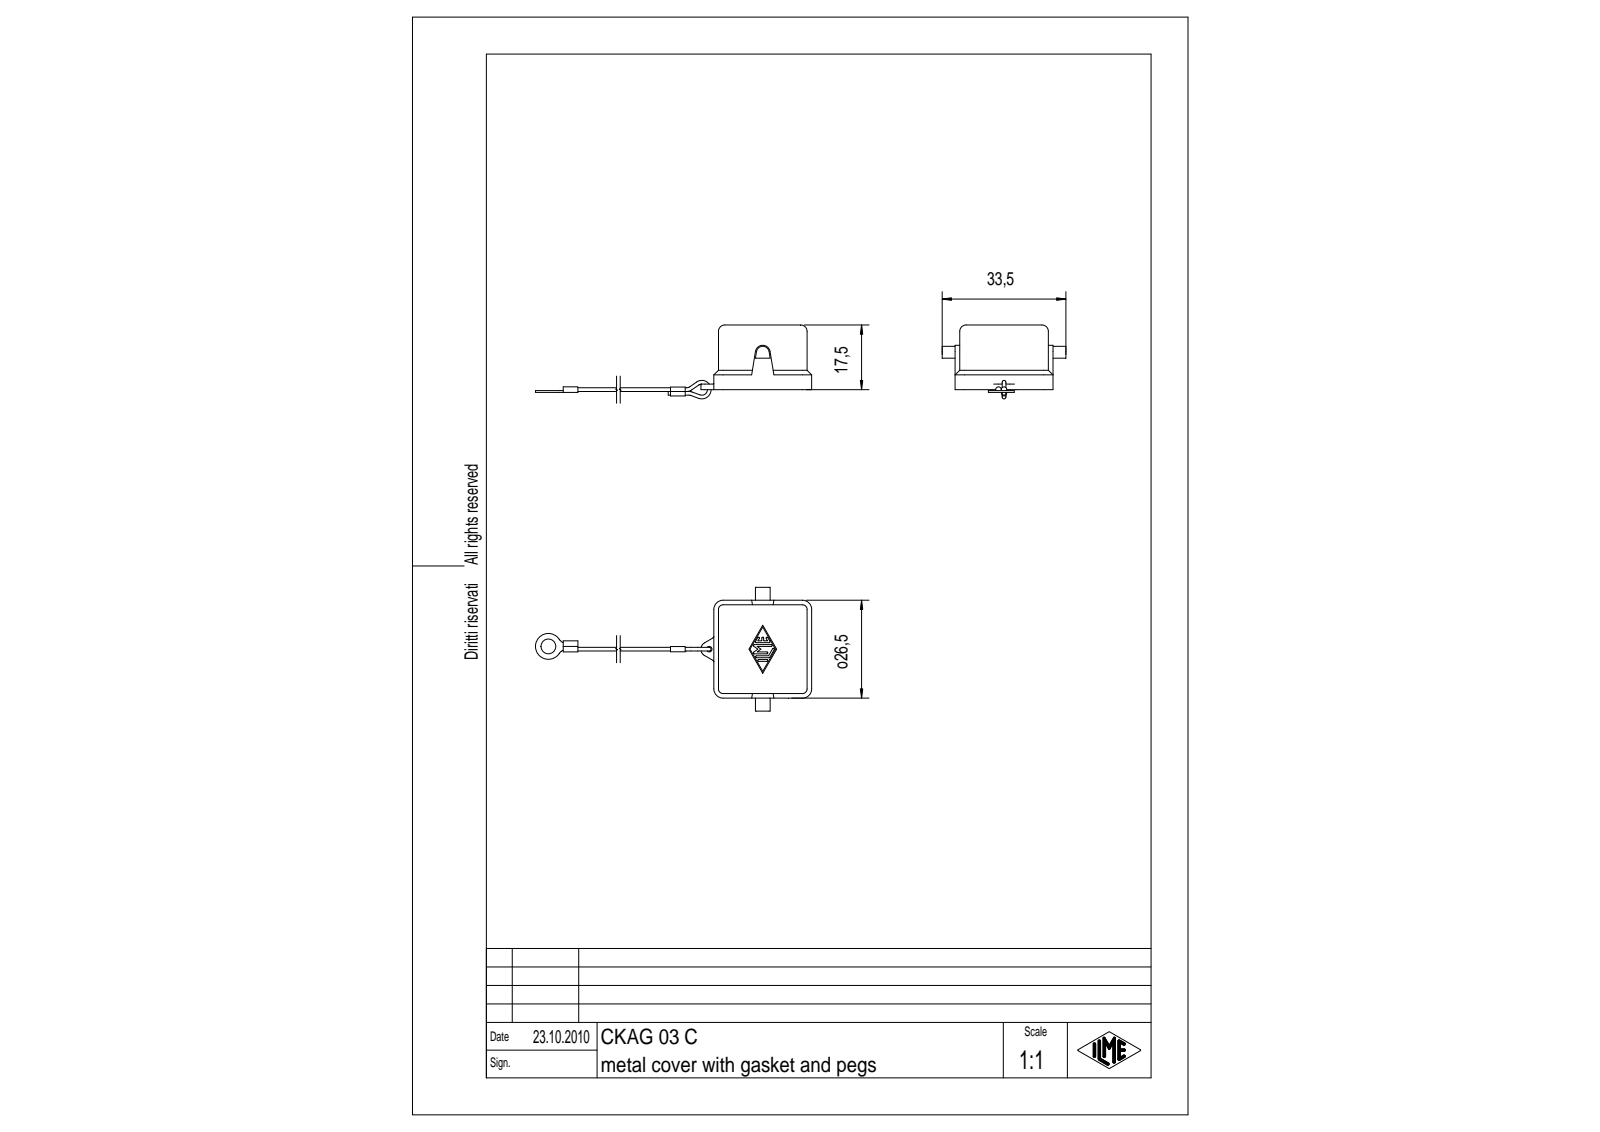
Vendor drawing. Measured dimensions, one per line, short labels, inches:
name: CKAG_03_C
written by: PTC Creo Elements/Direct Modeling 19.0E 27-Jun-2016 (C) Parametric Technology GmbH (AUTOMOTIVE_DESIGN)
unit: in
bodies: 1 solid, 220 faces (113 planar, 83 cylindrical, 24 other)
size: 5.148 × 1.319 × 0.787
volume: 0.255 in³; area: 8.516 in²
holes: 1× ⌀0.059, 1× ⌀0.157
bosses: 4× ⌀0.039, 1× ⌀0.276
rounds: 14× R0.01, 12× R0.069, 10× R0.079, 7× R0.008, 4× R0.049, 4× R0.098, 4× R0.126, 2× R0.02
face distances: 0.049, 0.896, 0.945, 0.846, 0.098, 0.079, 0.994, 0.148, 0.797, 0.059
hole spacings: 3.917
